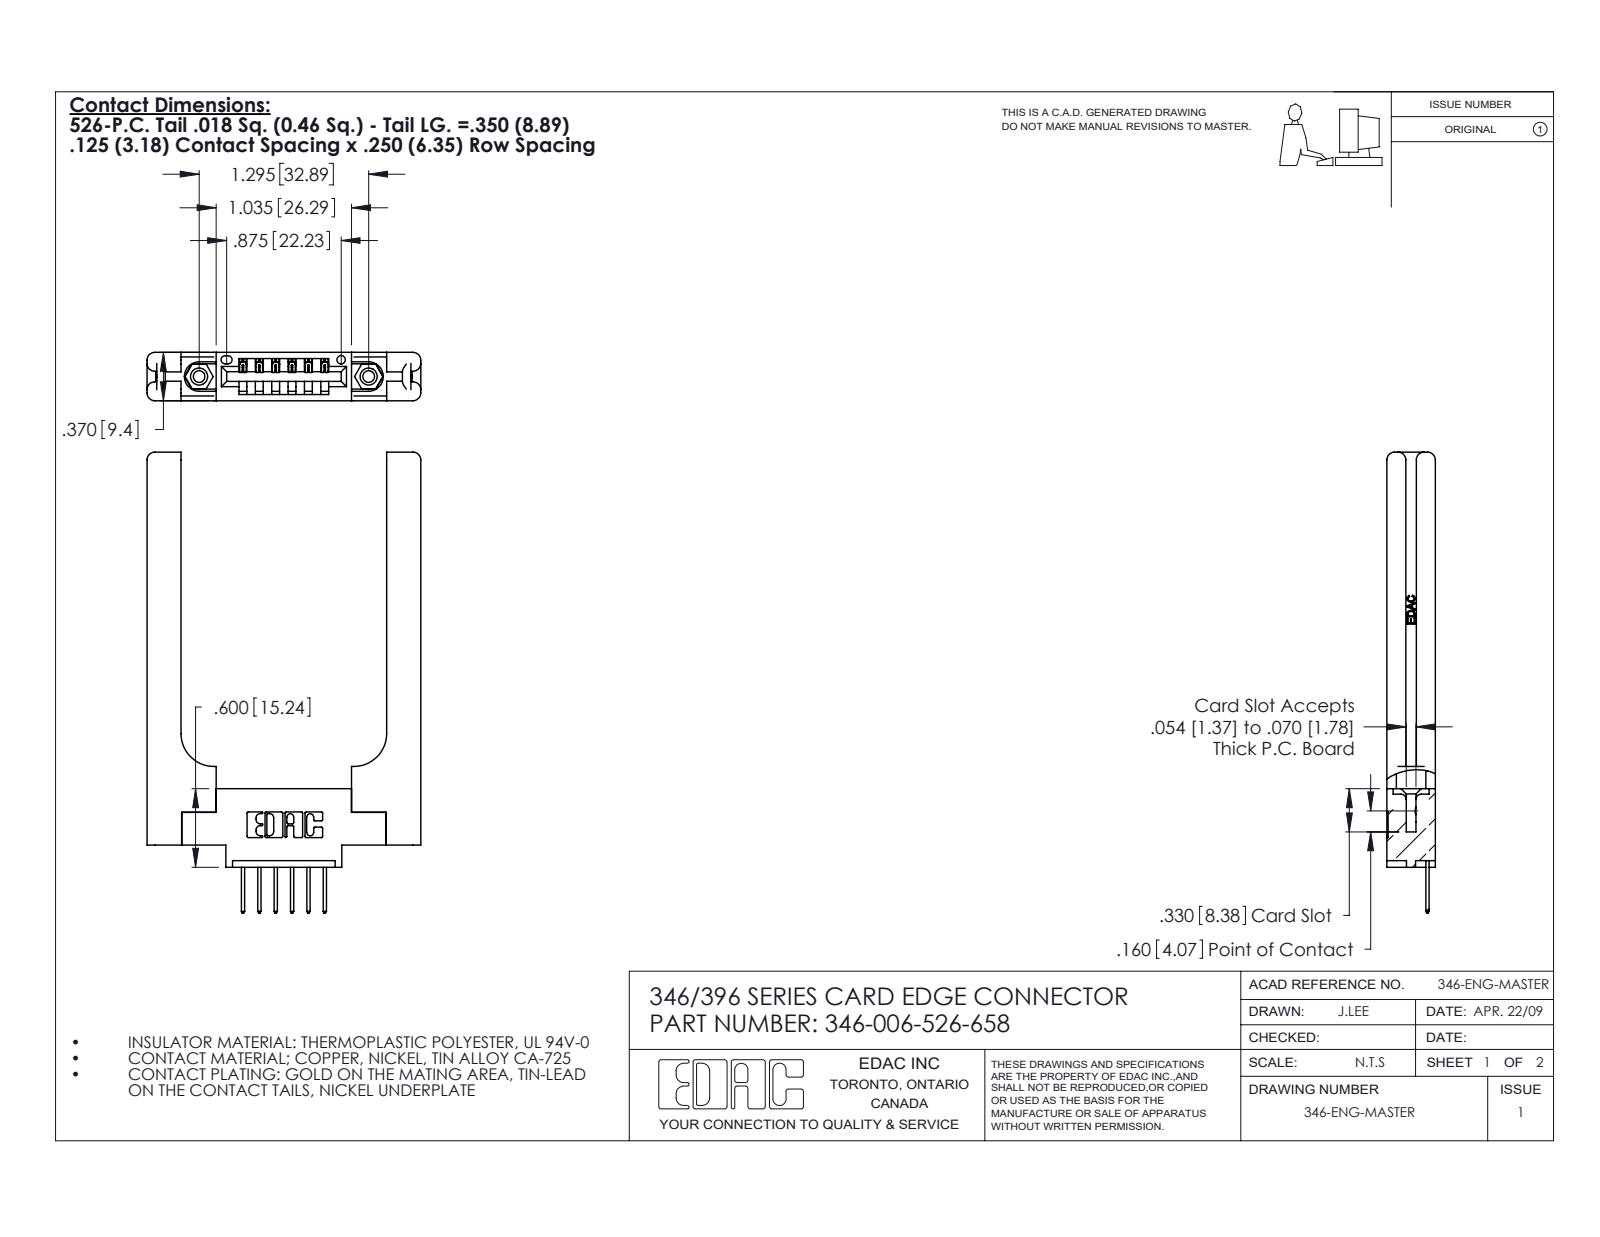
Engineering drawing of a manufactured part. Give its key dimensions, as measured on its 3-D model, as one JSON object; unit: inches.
{"part_name": "346-220-058_345-220-058; 345-292-001_345-293-126; 346-006-526-658; 346 Part_0.170 Offset - 0.156 Dia-TH (+1 more)", "step_written_by": "SolidWorks 2020 (CONFIG_CONTROL_DESIGN)", "units": "inches", "bodies": {"solids": 11, "faces": 744, "planar": 482, "cylindrical": 202, "other": 60}, "overall_size": [3.52, 2.091, 0.37], "volume_in3": 0.743, "surface_area_in2": 16.72, "round_holes": [[0.089, 2], [0.125, 2], [0.156, 2], [0.064, 1]], "round_bosses_or_shafts": [[0.155, 2]], "partial_cylinders_radius": [[0.01, 22], [0.06, 16], [0.006, 12], [0.01, 12], [0.007, 6], [0.031, 6], [0.026, 3], [0.03, 2]], "face_to_face_distances": [0.37, 0.15, 0.22, 0.072, 0.148, 0.25, 1.571, 0.071, 0.048, 0.322], "hole_center_spacings": [0.246, 1.092, 1.295]}
